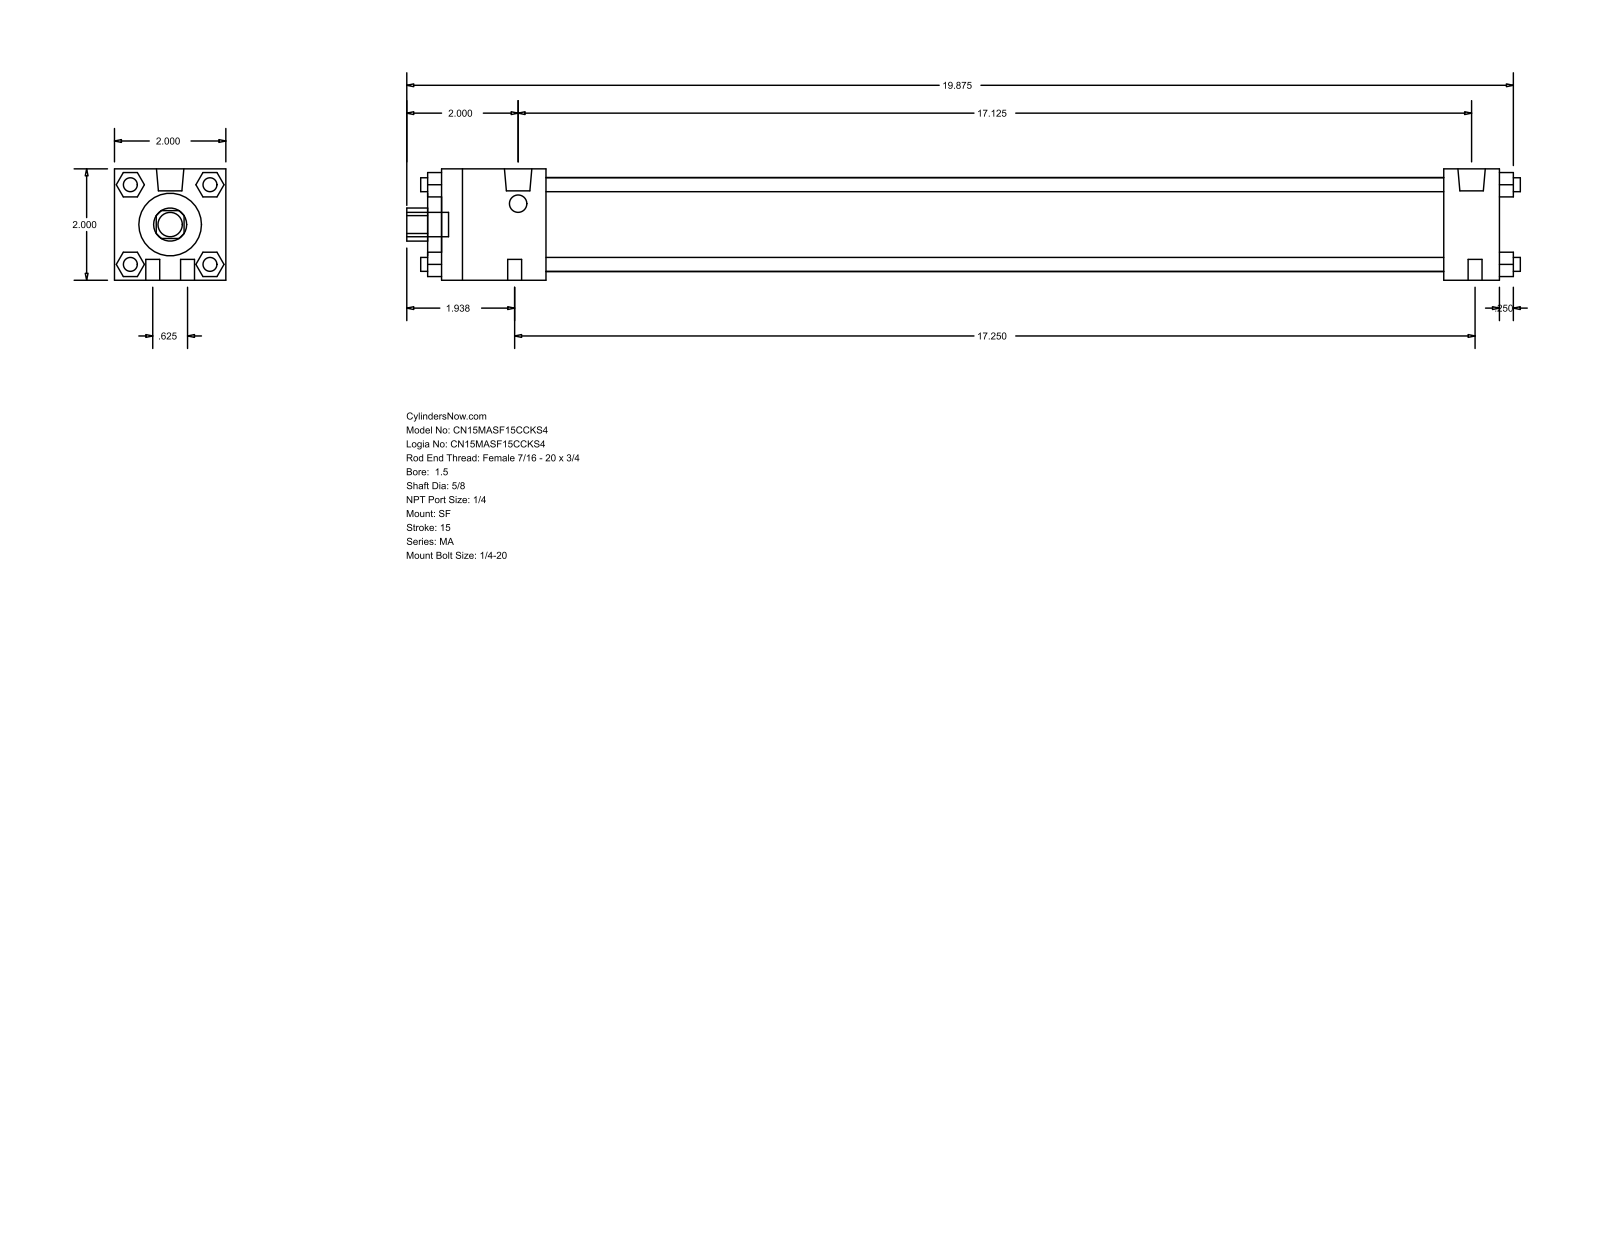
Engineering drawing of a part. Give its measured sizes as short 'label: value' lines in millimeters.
name: MA_SF__0150_0.625
written by: GSSL Pune (CONFIG_CONTROL_DESIGN)
unit: mm
bodies: 0 solids, 124 faces (94 planar, 30 cylindrical, 0 other)
size: 508 × 50.8 × 50.8
holes: 1× ⌀15.88, 1× ⌀28.57, 1× ⌀42.93
bosses: 8× ⌀6.35, 2× ⌀12.49, 2× ⌀7.94, 1× ⌀11.11
rounds: 1× R7.54
face distances: 50.8, 482.6, 47.62, 457.19, 409.57, 434.98, 25.41, 6.35, 488.95, 53.97
